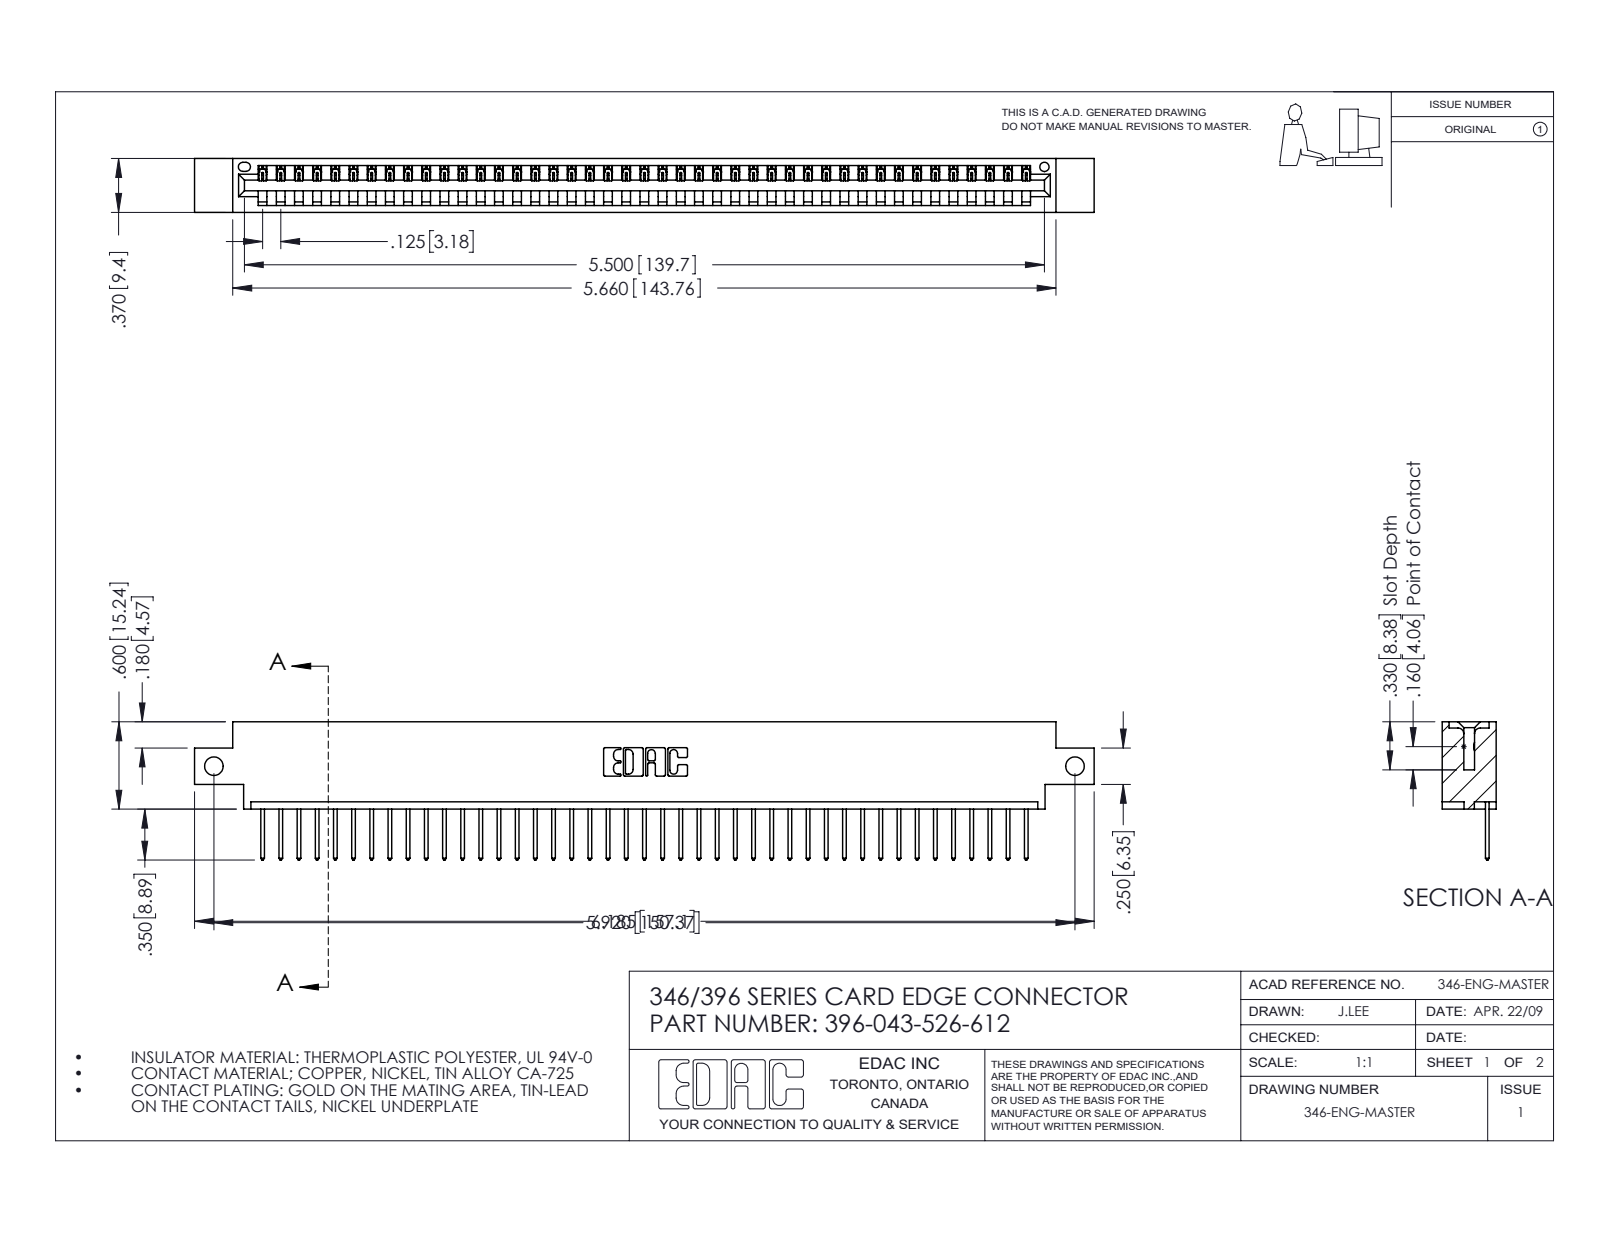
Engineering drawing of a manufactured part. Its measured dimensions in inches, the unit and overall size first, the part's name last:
Units: inches
Overall size (bounding box): 6.185 × 0.95 × 0.37
Round holes (diameter × count): ⌀0.128 ×2, ⌀0.064 ×1
Partial cylindrical surfaces — rounded edges, fillets, slot ends (radius × count): R0.006 ×86, R0.01 ×86, R0.01 ×22, R0.007 ×6, R0.031 ×6, R0.026 ×3, R0.031 ×2, R0.04 ×2
Main face-to-face distances: 0.048, 0.322, 0.37, 0.25, 0.072, 0.298, 0.025, 0.148, 0.222, 0.1
Hole centre spacings: 5.92
Volume: 0.901 in³ · Surface area: 28.59 in²
Bodies: 44 solids, 2620 faces (1800 planar, 820 cylindrical, 0 other)
Part name (STEP PRODUCT): 396-043-526-612; 346 Part_0.170 Offset - Side Mount; 345-292-001_345-293-126
STEP written by: SolidWorks 2016 (CONFIG_CONTROL_DESIGN)
